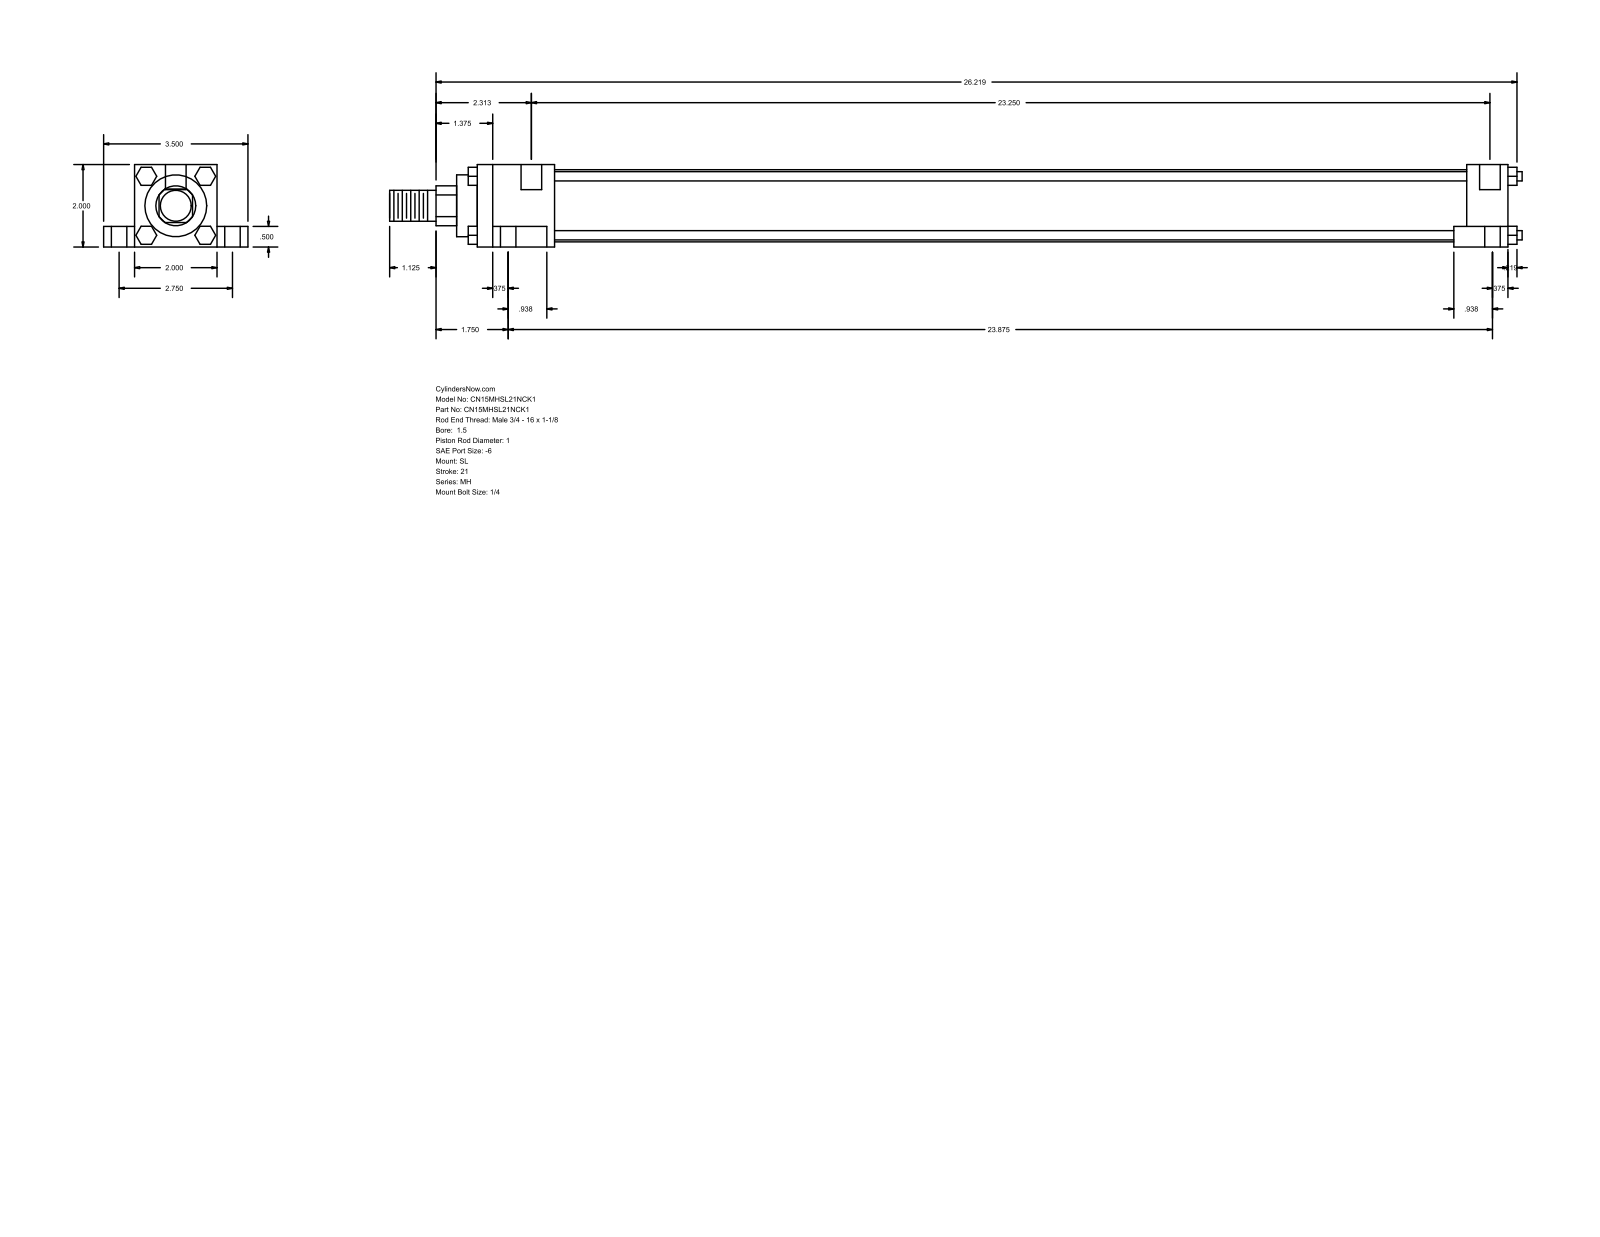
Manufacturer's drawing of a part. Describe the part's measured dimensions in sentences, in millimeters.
The part is named "MH_SL__0150_1". Its 3-D file was written by "GSSL Pune (CONFIG_CONTROL_DESIGN)". It is 0 solids with 148 faces: 112 planar, 36 cylindrical and 0 other. Overall it measures 697.71 by 88.9 by 50.8 millimeters. Round holes: 4 of diameter 5.56, 4 of diameter 9.53, 4 of diameter 15.88, 2 of diameter 12.7. Round bosses or shafts: 4 of diameter 5.71, 1 of diameter 44.45, 1 of diameter 38.1, 1 of diameter 25.4, 1 of diameter 19.05. Partial cylindrical surfaces (rounded edges, fillets, slot ends): 1 of radius 12.29. The main face-to-face distances are 50.8, 12.7, 38.1, 19.05, 69.85, 635, 25.4, 9.52, 33.34, 592.14. The hole center spacings are 34.96, 36.64, 37.73, 69.84, 593.17, 593.73, 596.34, 605.85.
